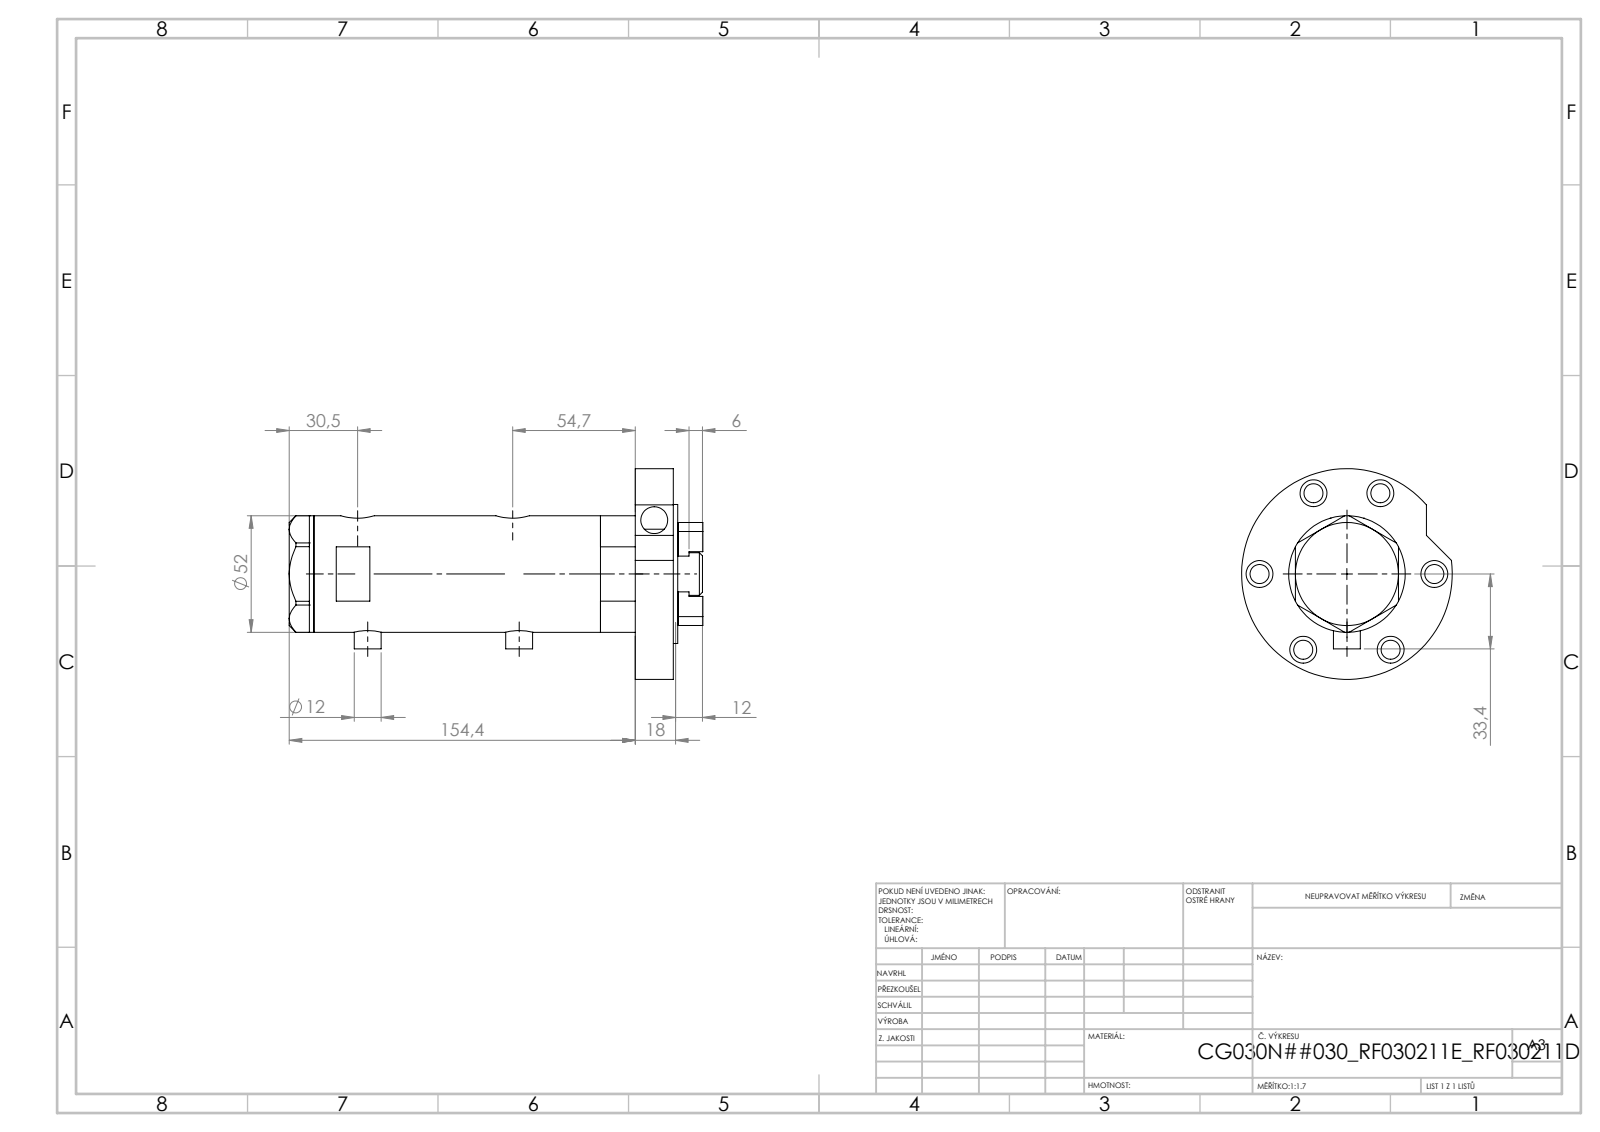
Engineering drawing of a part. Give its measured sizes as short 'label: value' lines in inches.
name: V270CG_VC; V270CG_RF211E; V270CG_MIDDLE; V270CG_FRONT (+2 more)
written by: SolidWorks 2019 (CONFIG_CONTROL_DESIGN)
unit: in
bodies: 7 solids, 224 faces (102 planar, 102 cylindrical, 20 other)
size: 7.056 × 3.701 × 3.701
volume: 24.75 in³; area: 157.9 in²
holes: 7× ⌀0.472, 6× ⌀0.335, 4× ⌀0.201, 4× ⌀0.354, 2× ⌀0.197, 2× ⌀0.383, 2× ⌀0.492, 2× ⌀0.591, 1× ⌀0.256, 1× ⌀0.787, 1× ⌀0.846, 1× ⌀1.181
bosses: 2× ⌀0.472, 1× ⌀3.701, 1× ⌀2.441, 1× ⌀2.047, 1× ⌀1.496, 1× ⌀0.748
face distances: 0.669, 5.333, 6.002, 0.079, 6.081, 0.433, 0.748, 0.937, 4.395, 5.065
hole spacings: 1.535, 0.659, 1.479, 1.843, 0.114, 0.177, 0.394, 0.881
